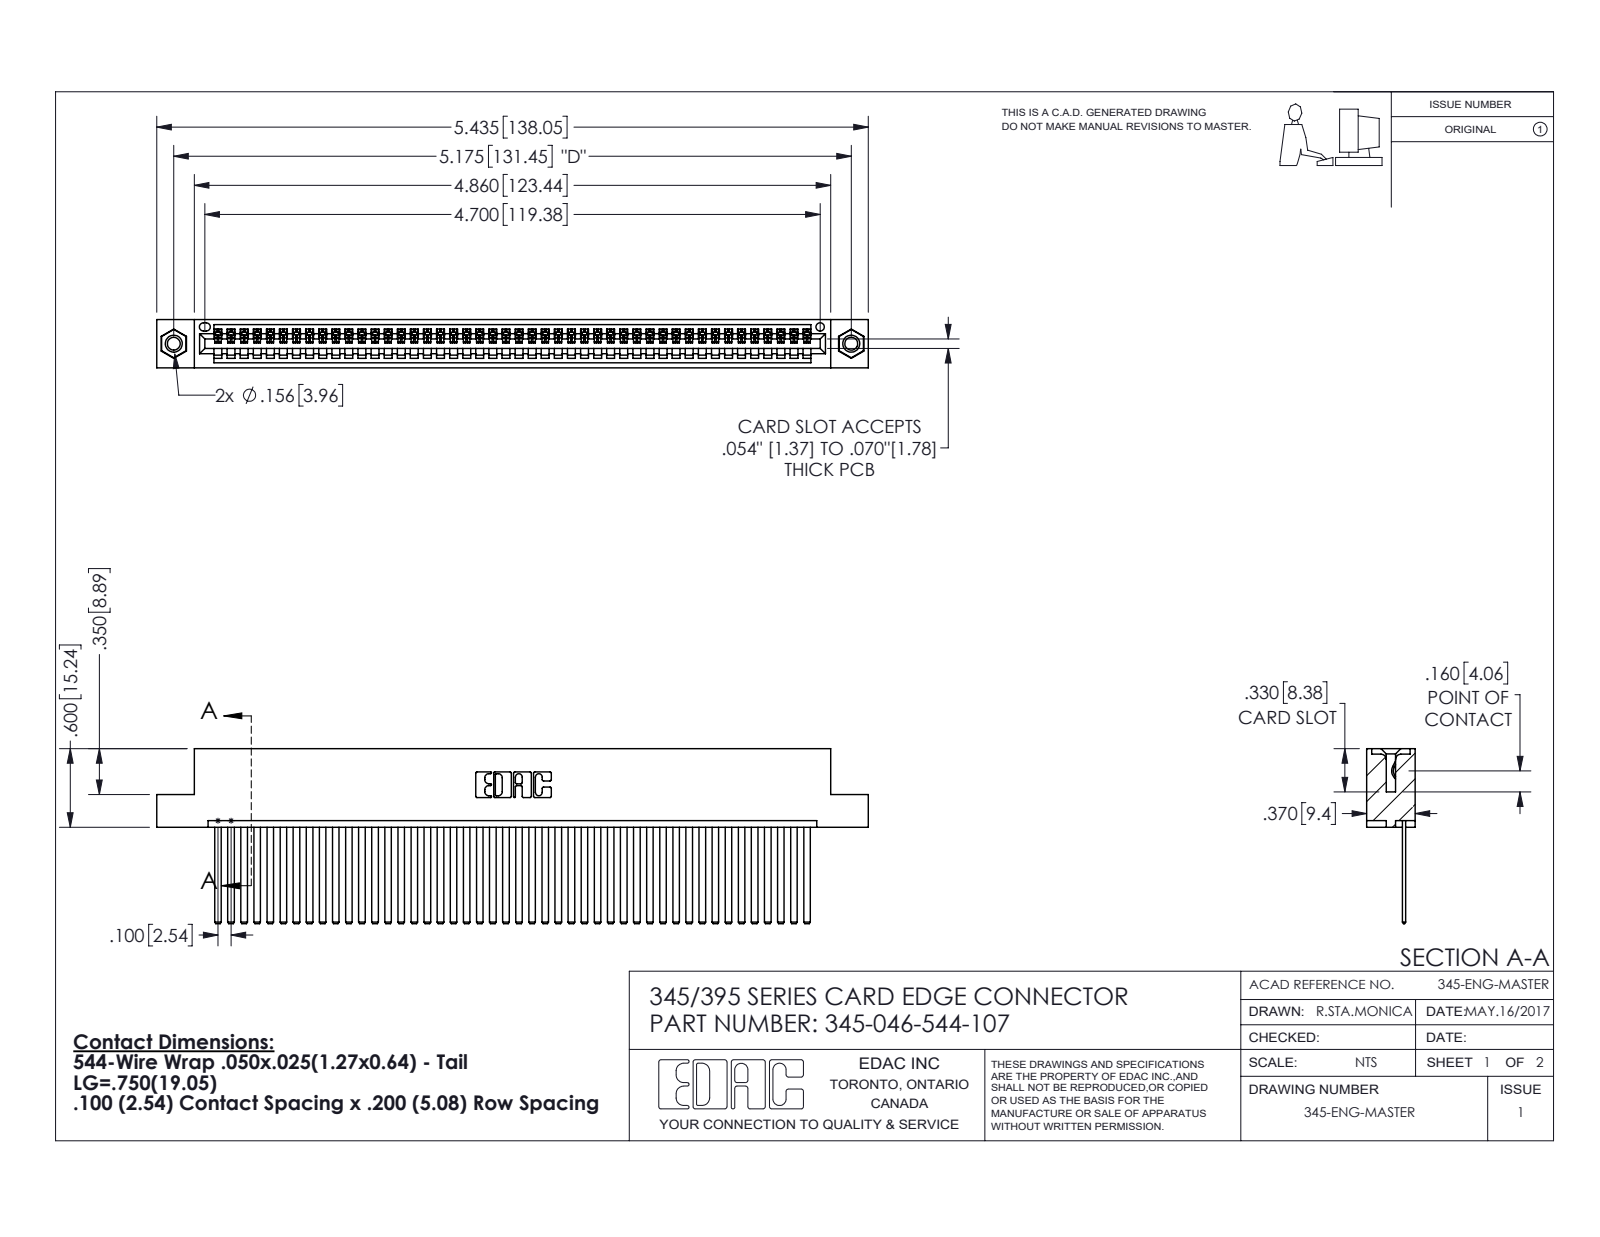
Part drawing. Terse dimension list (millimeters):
name: 345 Part_Flush Mounting Lugs - 0.156 Dia-TI; 345-046-544-107; 345-250-001_345-250-005-103; 345-292-001_345-293-144
written by: SolidWorks 2016 (CONFIG_CONTROL_DESIGN)
unit: mm
bodies: 49 solids, 2578 faces (1768 planar, 794 cylindrical, 16 other)
size: 138 × 34 × 9.4
volume: 13 700 mm³; area: 19 850 mm²
holes: 2× ⌀2.5, 2× ⌀3.2, 2× ⌀4, 1× ⌀1.6
bosses: 2× ⌀3.9
rounds: 92× R0.2, 22× R0.3, 6× R0.2, 6× R0.8, 3× R0.7, 2× R0.8, 2× R1, 1× R0.4
face distances: 1.8, 7.6, 0.6, 2.5, 6.9, 9.4, 5.1, 5.7, 3.8, 1.8
hole spacings: 6.9, 125.5, 131.4
